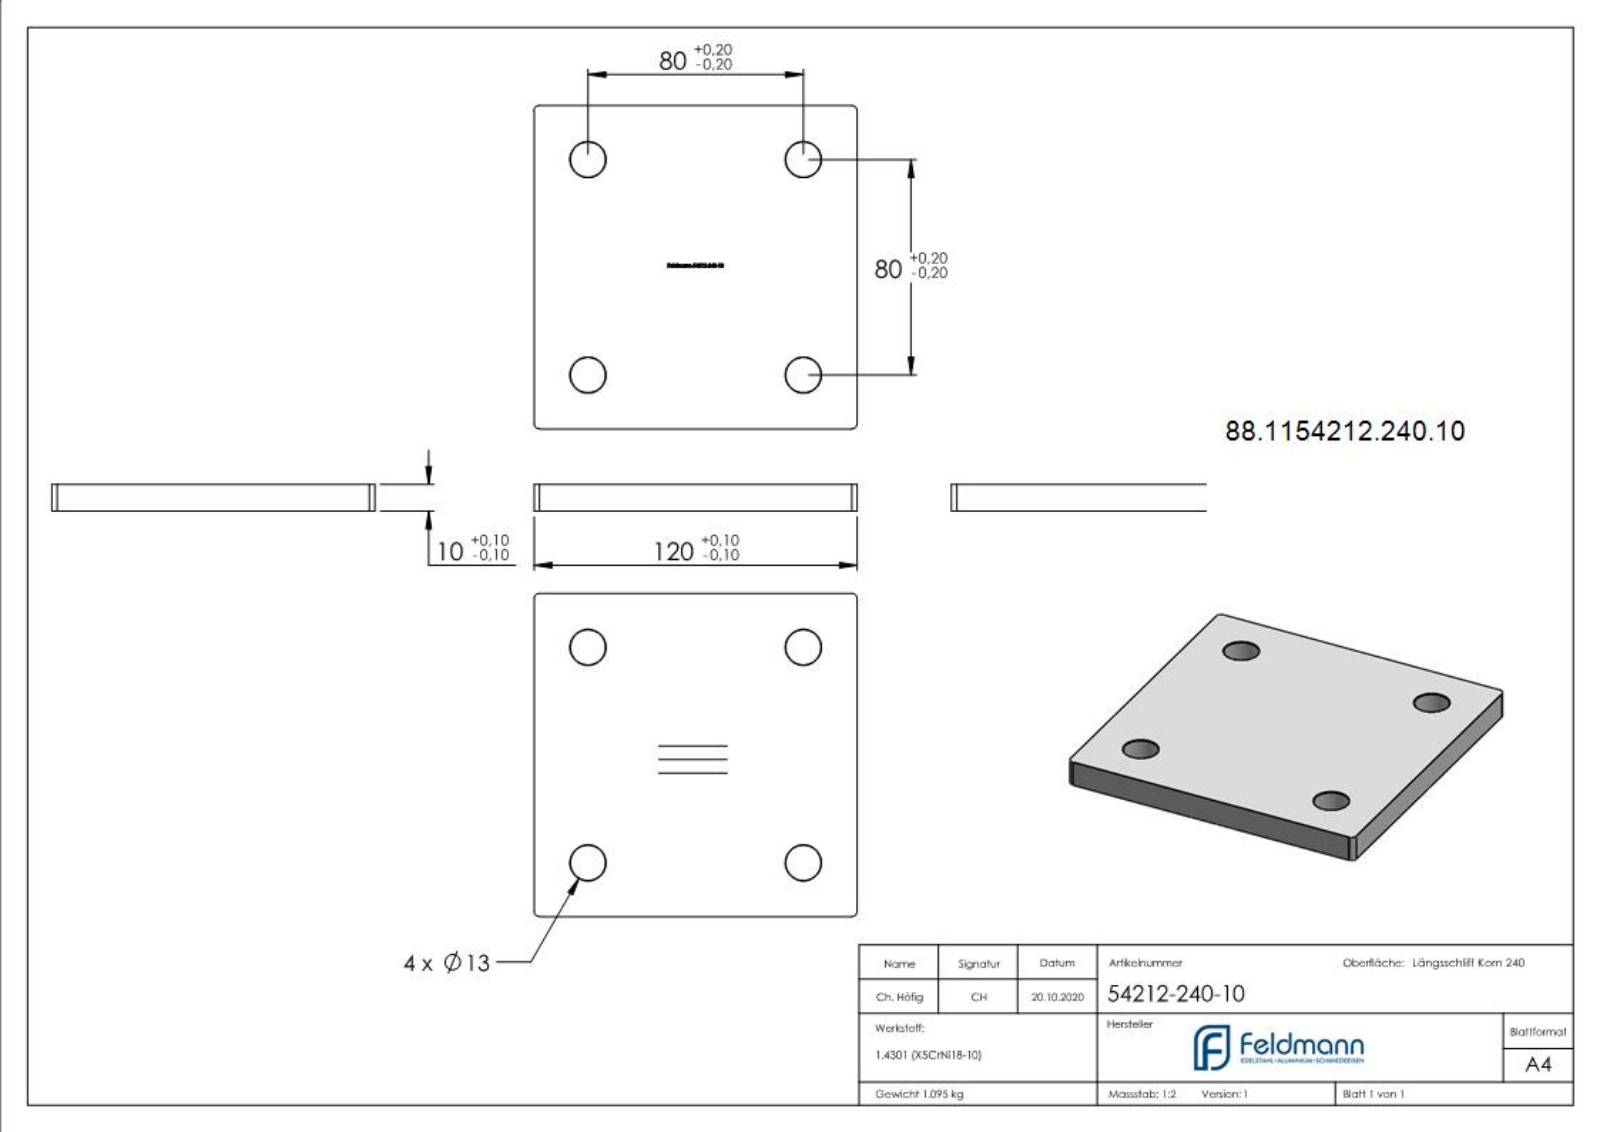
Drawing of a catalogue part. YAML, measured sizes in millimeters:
part_name: "54212-240-10"
step_written_by: "SolidWorks 2018 (CONFIG_CONTROL_DESIGN)"
units: millimeters
bodies: {solids: 1, faces: 277, planar: 157, cylindrical: 12, other: 108}
overall_size: [120, 120, 10]
volume: 138645
surface_area: 34094
round_holes:
  - {diameter: 13, count: 4}
partial_cylinders:
  - {radius: 2, count: 4}
face_to_face_distances: [10, 120, 9.9, 60, 0.44, 0.88, 1.19, 10.74, 17.05, 6.31]
hole_center_spacings: [80, 113.14]
